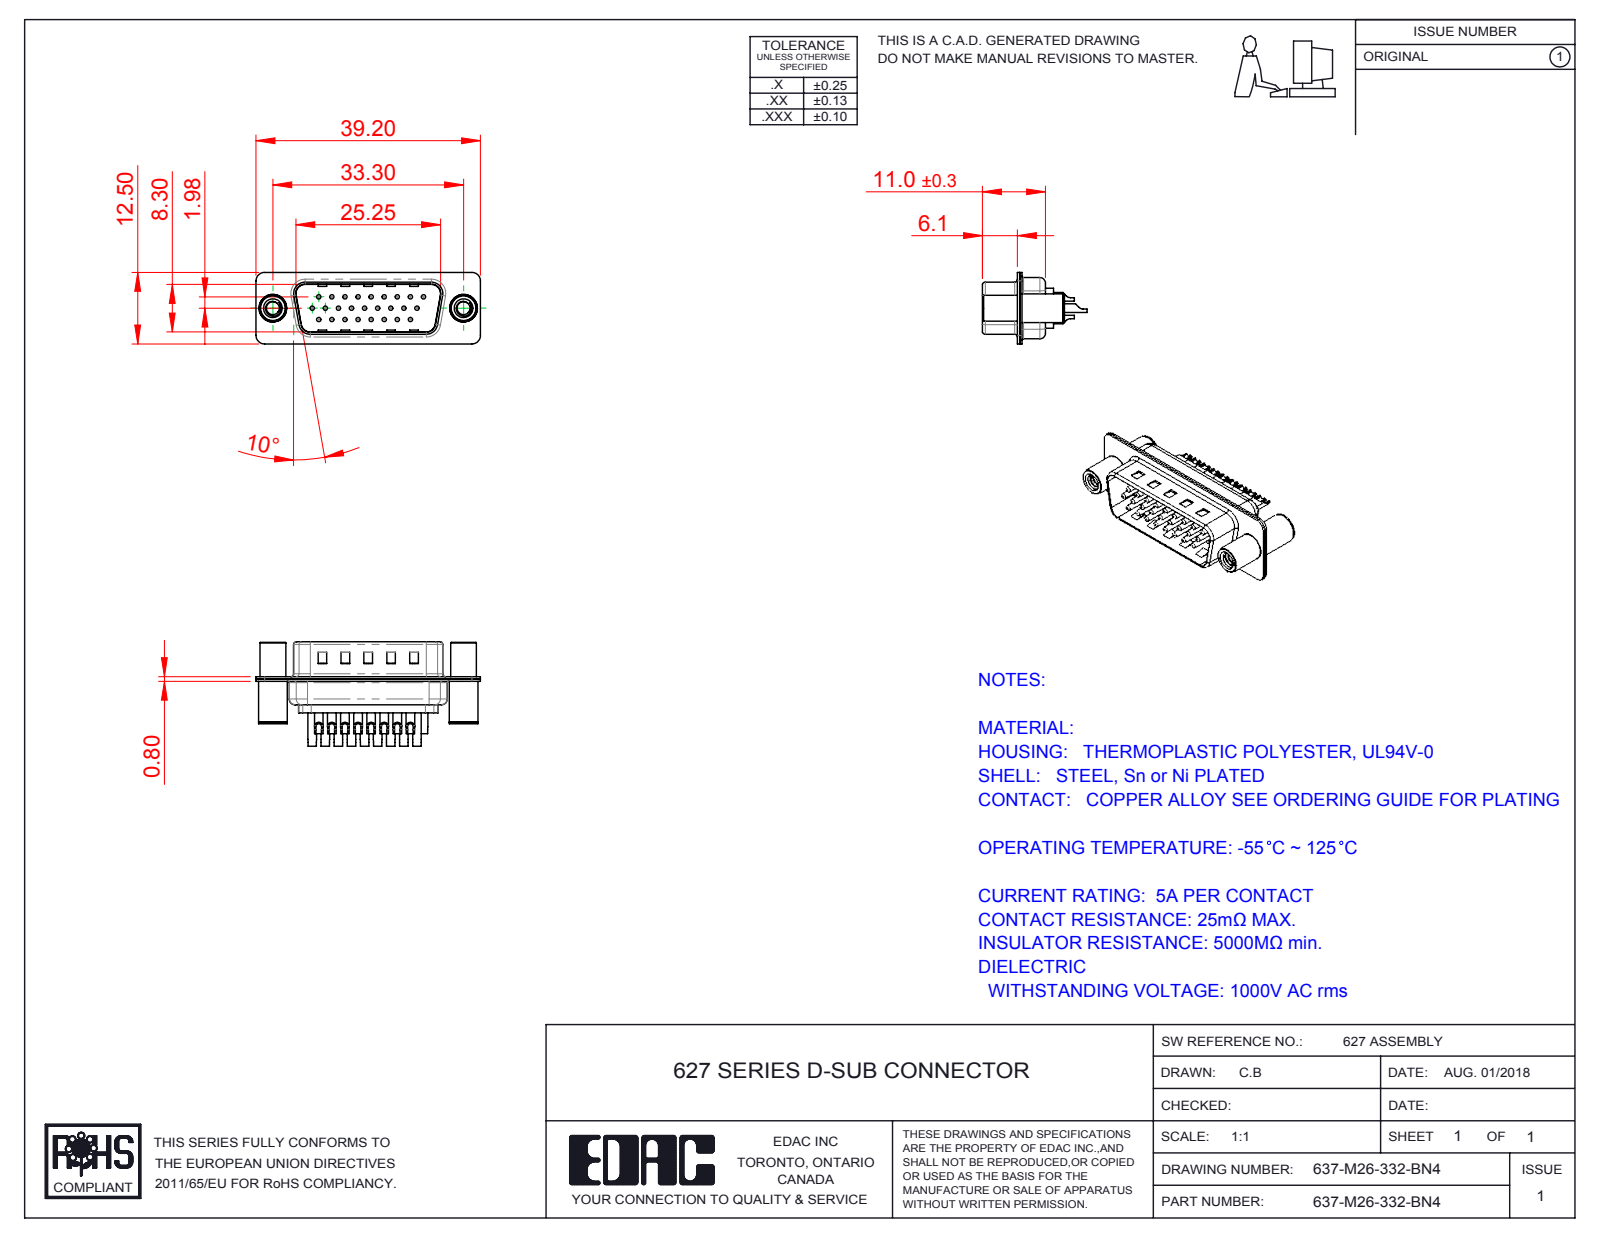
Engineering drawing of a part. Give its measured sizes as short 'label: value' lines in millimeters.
name: 637M Contact Row 1_32; 637M Contact Row 2_32; 637M Shell Front_26 Contacts; 637M Contact Row 3_32 (+4 more)
written by: SolidWorks 2016 (CONFIG_CONTROL_DESIGN)
unit: mm
bodies: 31 solids, 1388 faces (379 planar, 601 cylindrical, 408 other)
size: 39.2 × 18.25 × 12.5
volume: 2 283 mm³; area: 6 602 mm²
holes: 26× ⌀0.75, 26× ⌀1, 26× ⌀1.6, 26× ⌀2, 2× ⌀2.26, 2× ⌀3.26, 2× ⌀4, 2× ⌀4.8
bosses: 26× ⌀1.5, 2× ⌀5, 2× ⌀4.9, 2× ⌀4.5
rounds: 16× R1.5, 12× R2, 8× R0.5, 8× R1.6, 7× R1, 4× R0.25, 4× R0.6, 4× R0.65
face distances: 0.4, 0.8, 9.5, 9.1, 8.7, 9.9, 0.75, 0.35, 1.2, 1.9
hole spacings: 3.96, 2.28, 4.57, 6.05, 2.29, 8.24, 6.86, 10.48
